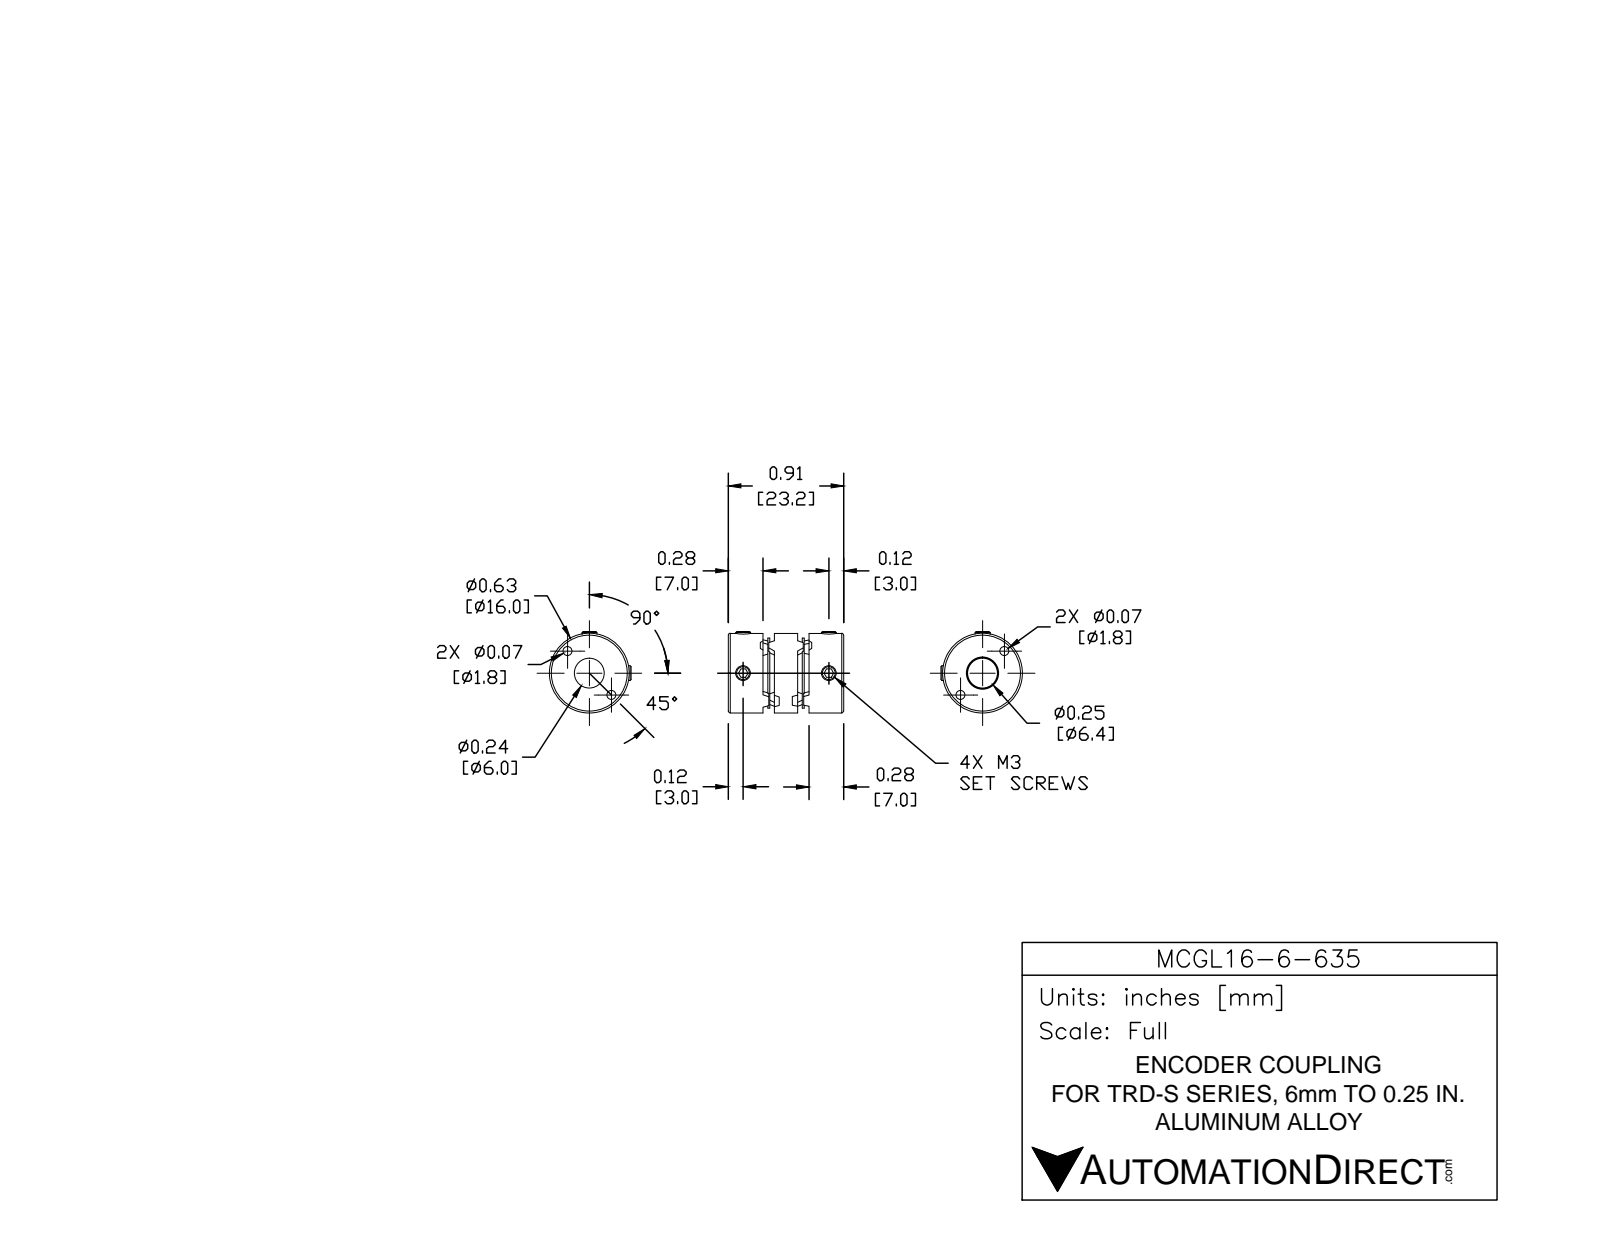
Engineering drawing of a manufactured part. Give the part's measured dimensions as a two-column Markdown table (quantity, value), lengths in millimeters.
| quantity | value |
| --- | --- |
| part name | MCGL16-6-635 |
| STEP written by | SolidWorks 2016 (AUTOMOTIVE_DESIGN) |
| units | millimeters |
| bodies | 1 solid, 158 faces (86 planar, 36 cylindrical, 36 other) |
| overall size | 23 × 16 × 16 |
| volume | 3 131 mm³ |
| surface area | 3 177 mm² |
| round holes (diameter × count) | 3 × 4, 2.4 × 2, 6 × 1, 6.35 × 1, 6.6 × 1, 7.6 × 1 |
| round bosses / shafts (diameter × count) | 16 × 1 |
| main face-to-face distances | 1.5, 8, 6.5, 1, 7, 8.5, 15, 14.5, 0.5, 9.5 |
| hole center spacings | 5.9, 17, 11.8 |
